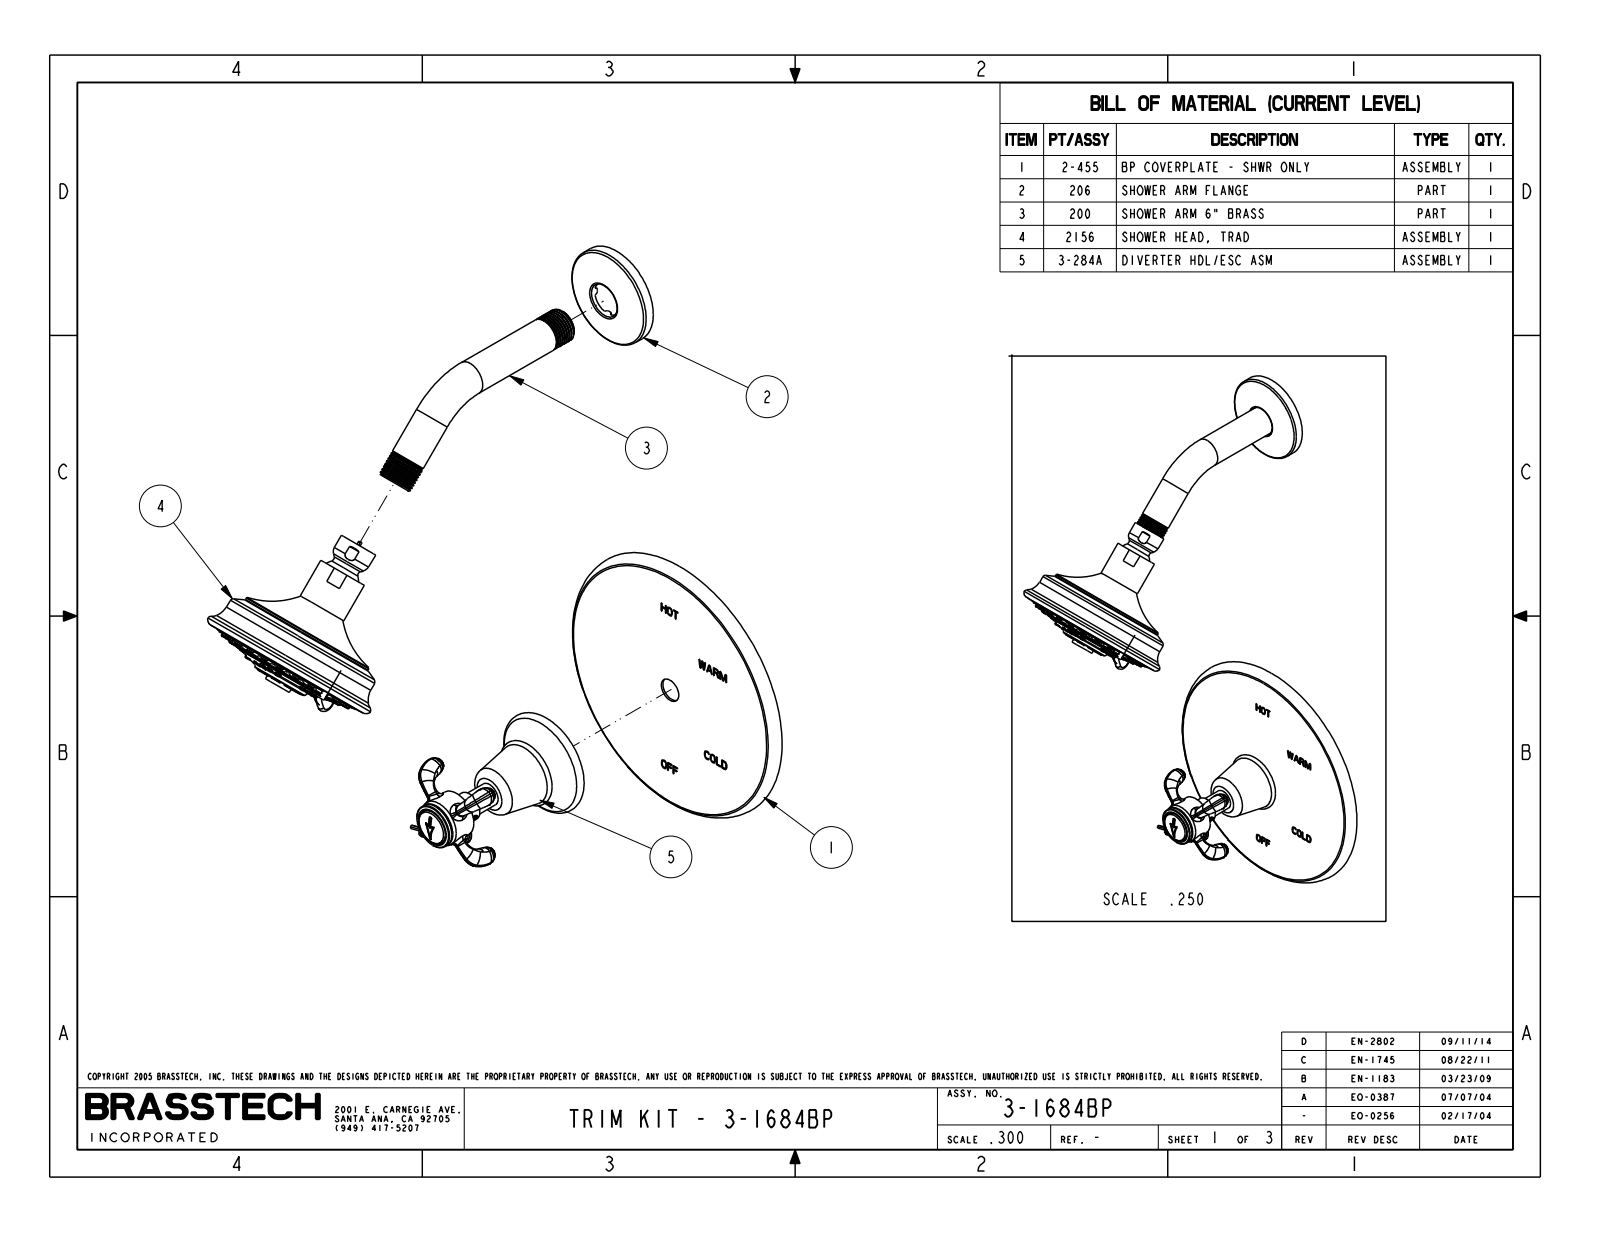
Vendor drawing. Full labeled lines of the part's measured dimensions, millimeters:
Part name (STEP PRODUCT): 11124; H-78; 2-455_ASM; 206 (+8 more)
STEP written by: PRO/ENGINEER BY PARAMETRIC TECHNOLOGY CORPORATION, 2013150 (CONFIG_CONTROL_DESIGN)
Units: millimetres
Bodies: 48 solids, 7735 faces (3432 planar, 1631 cylindrical, 2672 other)
Overall size (bounding box): 419.2 × 229.1 × 168.3
Volume: 251 400 mm³ · Surface area: 365 600 mm²
Round holes (diameter × count): ⌀1.1 ×32, ⌀2.5 ×15, ⌀1.5 ×12, ⌀2 ×8, ⌀2.4 ×8, ⌀4.7 ×8, ⌀3 ×7, ⌀3.8 ×3, ⌀6.4 ×3, ⌀7 ×3, ⌀3.5 ×2, ⌀6.8 ×2
Round bosses / shafts (diameter × count): ⌀3.6 ×39, ⌀4.2 ×23, ⌀8 ×3, ⌀6.2 ×3, ⌀20.7 ×2, ⌀19.5 ×2, ⌀5.8 ×2, ⌀4.2 ×2
Partial cylindrical surfaces — rounded edges, fillets, slot ends (radius × count): R0.5 ×52, R0.3 ×29, R2.1 ×15, R0.2 ×14, R2 ×9, R0.8 ×8, R2.2 ×8, R18.9 ×5
Main face-to-face distances: 1.3, 2.5, 5.3, 7.8, 2, 8, 0.5, 4.8, 12.1, 7.3
Hole centre spacings: 9.6, 10.7, 7, 5.3, 7, 9.4, 10.7, 15.4
